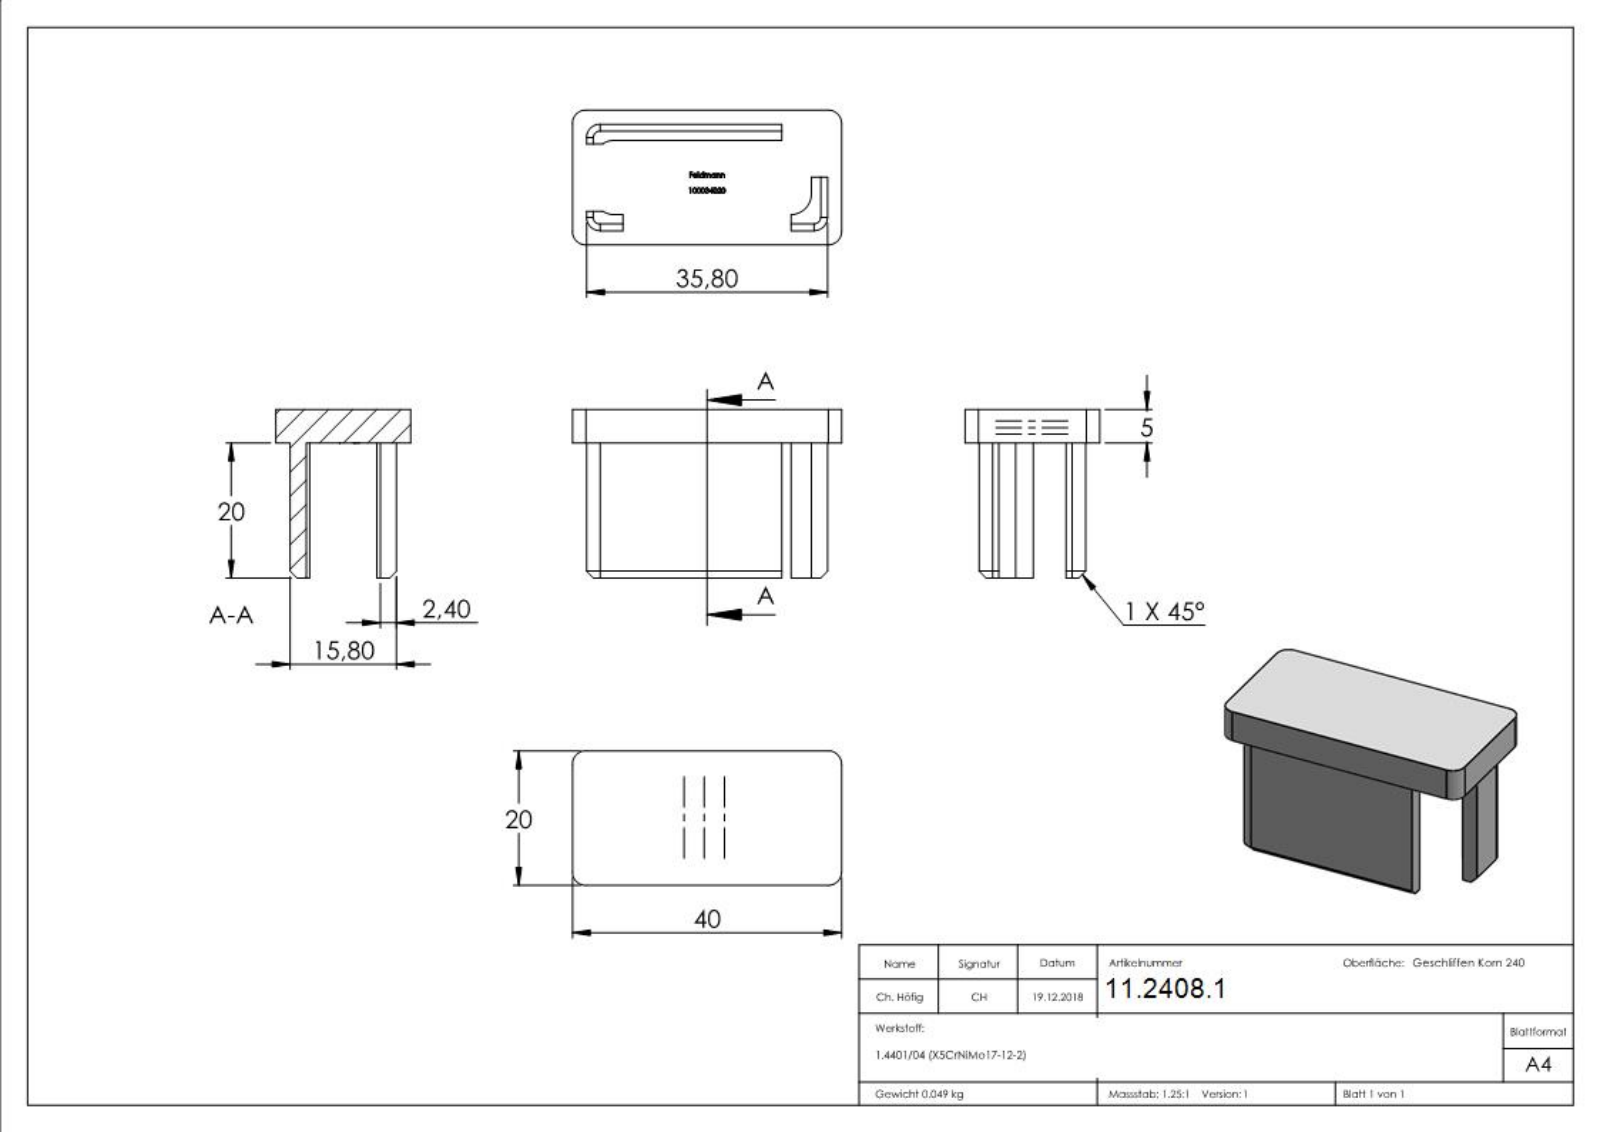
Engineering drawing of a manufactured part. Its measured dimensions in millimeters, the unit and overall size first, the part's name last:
Units: millimetres
Overall size (bounding box): 40 × 25 × 20
Partial cylindrical surfaces — rounded edges, fillets, slot ends (radius × count): R2 ×7, R3 ×3
Main face-to-face distances: 5, 2.4, 2.1, 17.9, 4.5, 20, 15.5, 13.4, 15.8, 5.4
Volume: 6 183 mm³ · Surface area: 4 199 mm²
Bodies: 1 solid, 264 faces (138 planar, 10 cylindrical, 116 other)
Part name (STEP PRODUCT): 100034020
STEP written by: SolidWorks 2015 (CONFIG_CONTROL_DESIGN)
